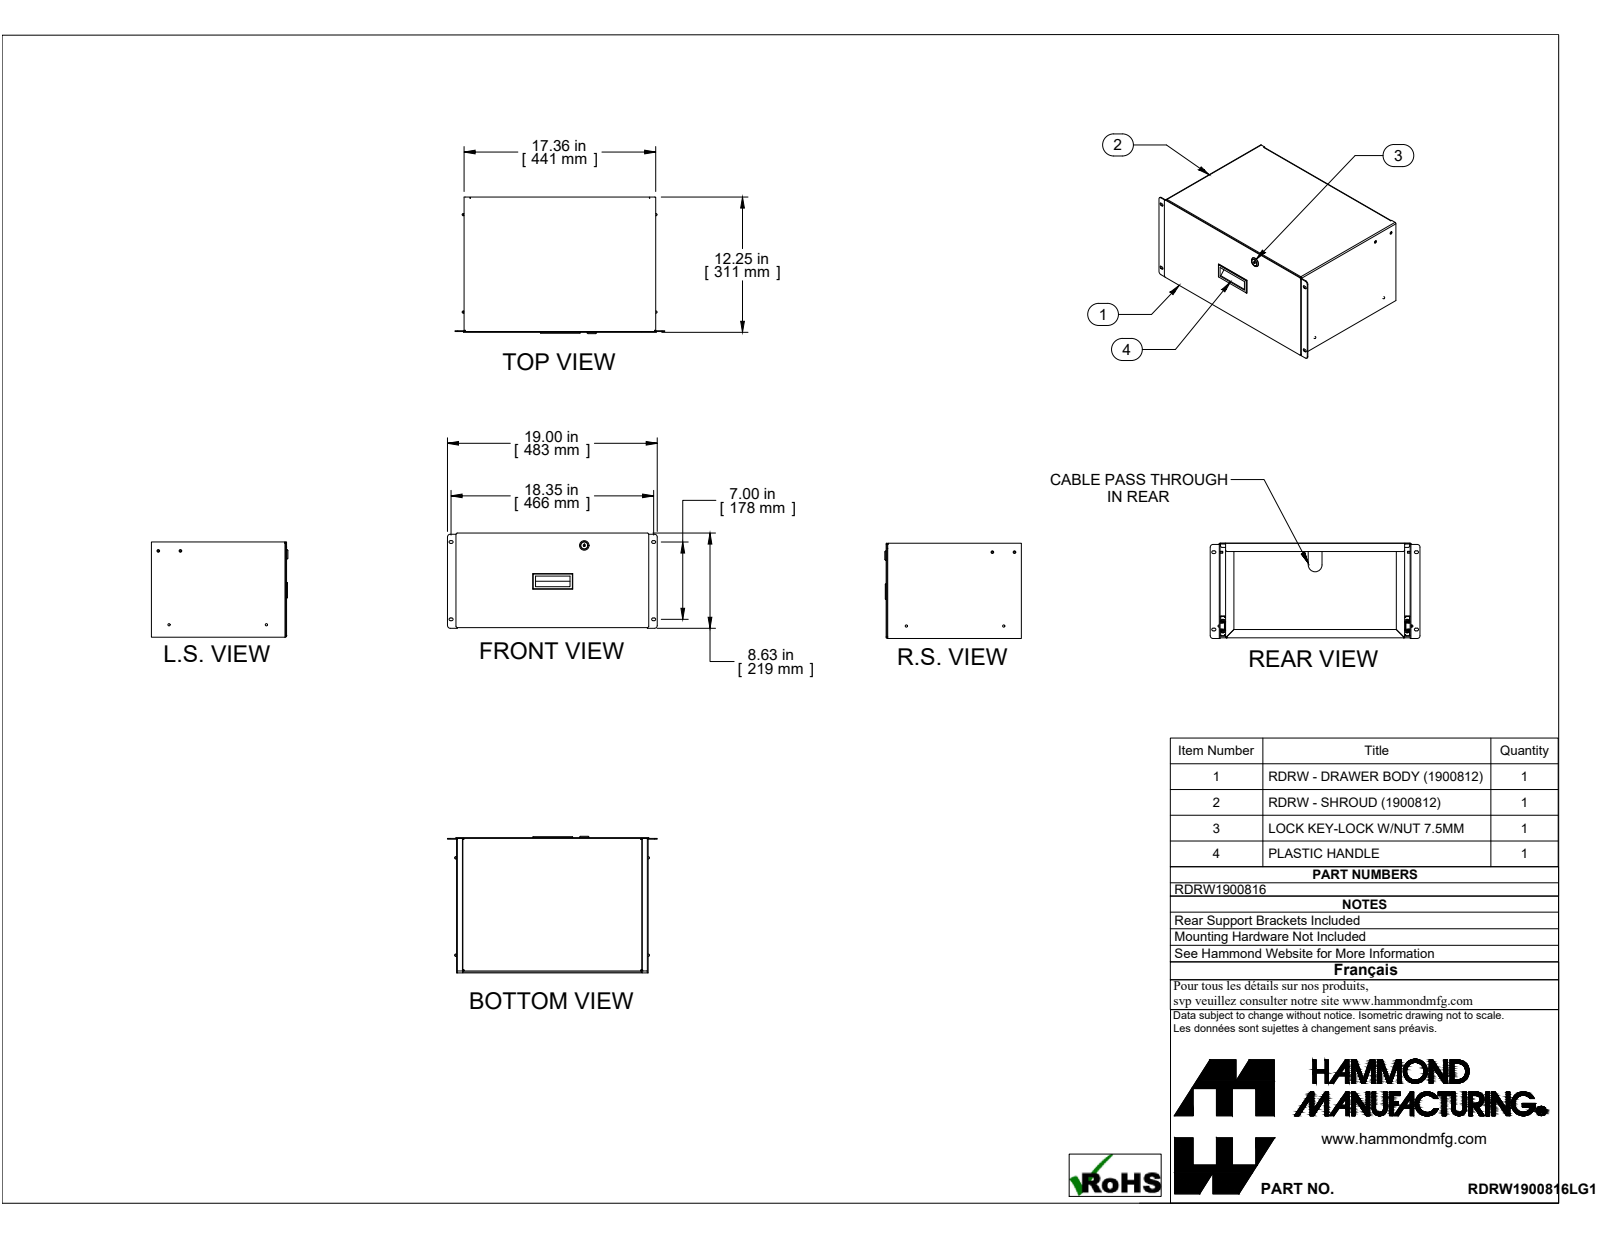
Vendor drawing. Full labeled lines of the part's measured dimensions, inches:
Part name (STEP PRODUCT): RDRW1900816LG1
STEP written by: SolidWorks 2019 (CONFIG_CONTROL_DESIGN)
Units: inches
Bodies: 24 solids, 682 faces (376 planar, 264 cylindrical, 42 other)
Overall size (bounding box): 19 × 16.395 × 8.626
Volume: 97.1 in³ · Surface area: 3 252 in²
Round holes (diameter × count): ⌀0.177 ×6, ⌀0.156 ×4, ⌀0.18 ×4, ⌀0.25 ×4, ⌀0.172 ×3, ⌀0.163 ×2, ⌀0.153 ×1, ⌀0.198 ×1, ⌀0.625 ×1
Round bosses / shafts (diameter × count): ⌀0.235 ×2, ⌀0.164 ×2, ⌀0.866 ×1, ⌀0.547 ×1, ⌀0.335 ×1
Partial cylindrical surfaces — rounded edges, fillets, slot ends (radius × count): R0.086 ×52, R0.029 ×40, R0.05 ×16, R0.125 ×16, R0.024 ×8, R0.072 ×8, R0.036 ×6, R0.1 ×6
Main face-to-face distances: 0.072, 0.048, 16.712, 0.5, 0.572, 16.784, 17.284, 8.491, 8.563, 8.443
Hole centre spacings: 0.38, 12.6, 0.36, 0.622, 0.74, 1.002, 1.26, 1.362
